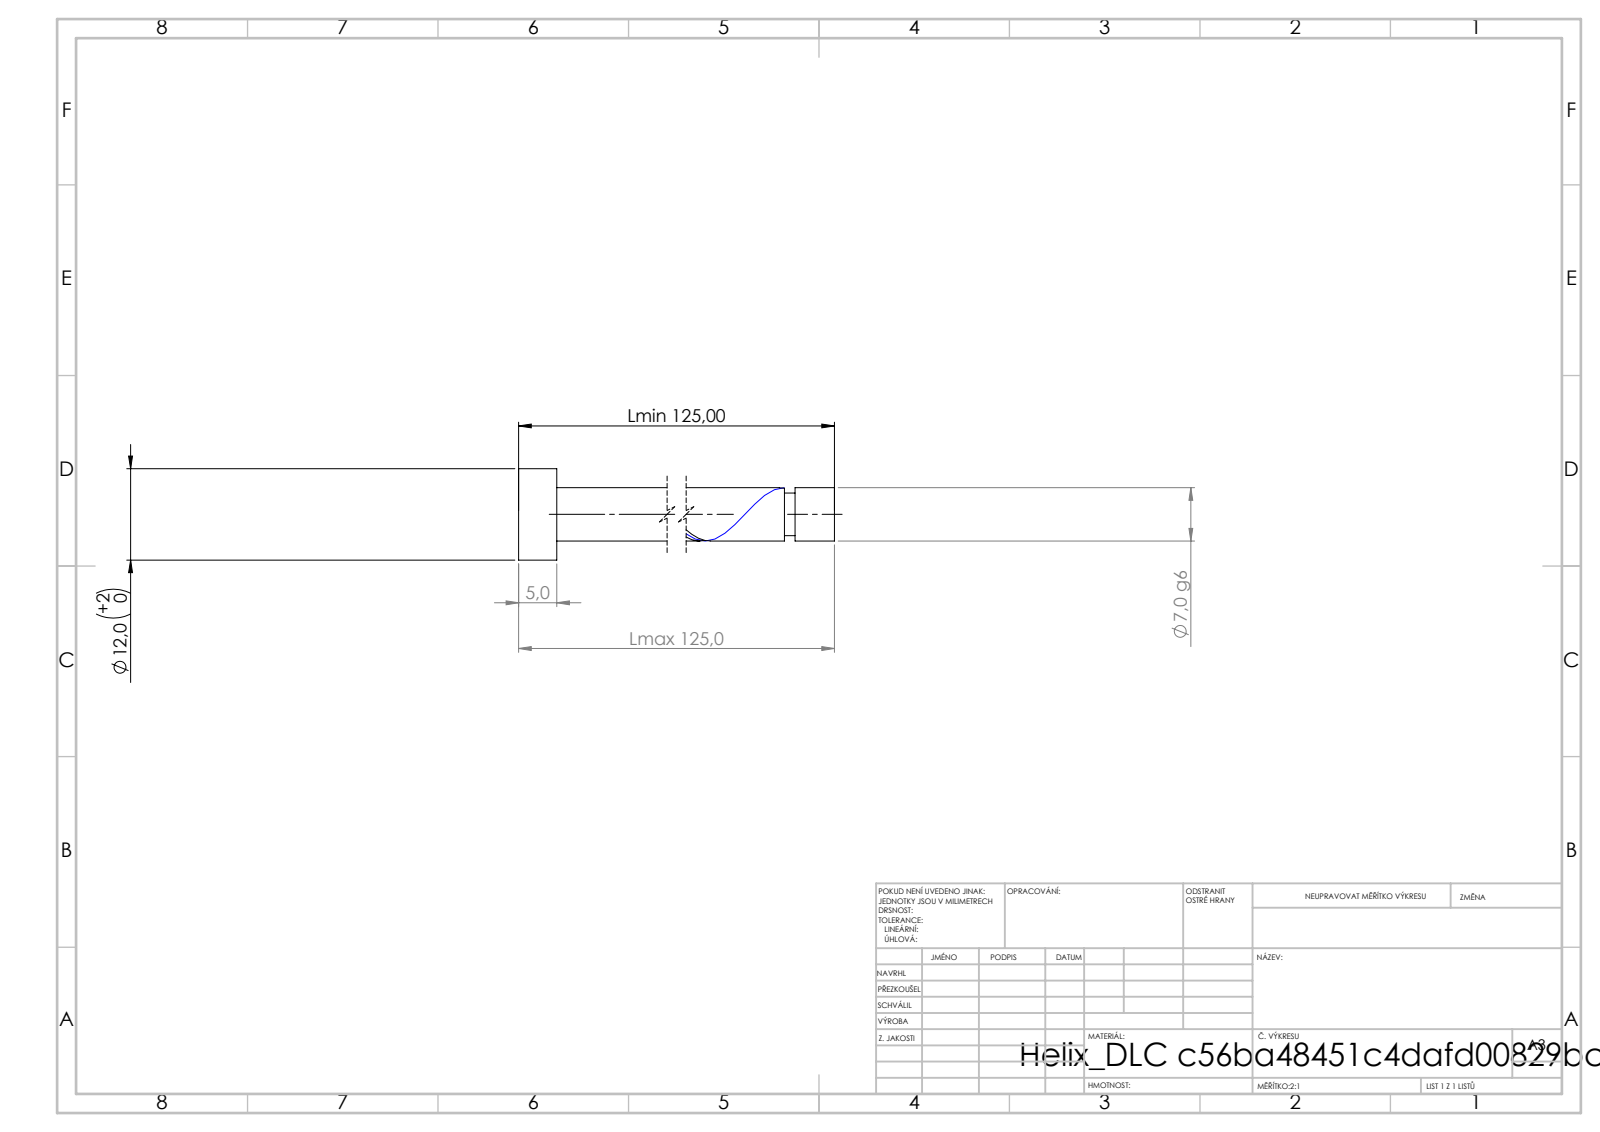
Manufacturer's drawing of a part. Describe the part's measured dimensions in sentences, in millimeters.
Its 3-D file was written by "SolidWorks 2019 (CONFIG_CONTROL_DESIGN)". It is 1 solid with 21 faces: 6 planar, 14 cylindrical and 1 other. Overall it measures 125 by 12 by 12 millimeters. Its volume is 5 118 cubic millimeters and its surface area 3 145 square millimeters. Round bosses or shafts: 1 of diameter 12, 1 of diameter 7, 1 of diameter 5.6. The main face-to-face distances are 5, 125, 120, 119.84, 114.84, 5.16, 118.44, 113.44, 1.4, 6.56.
